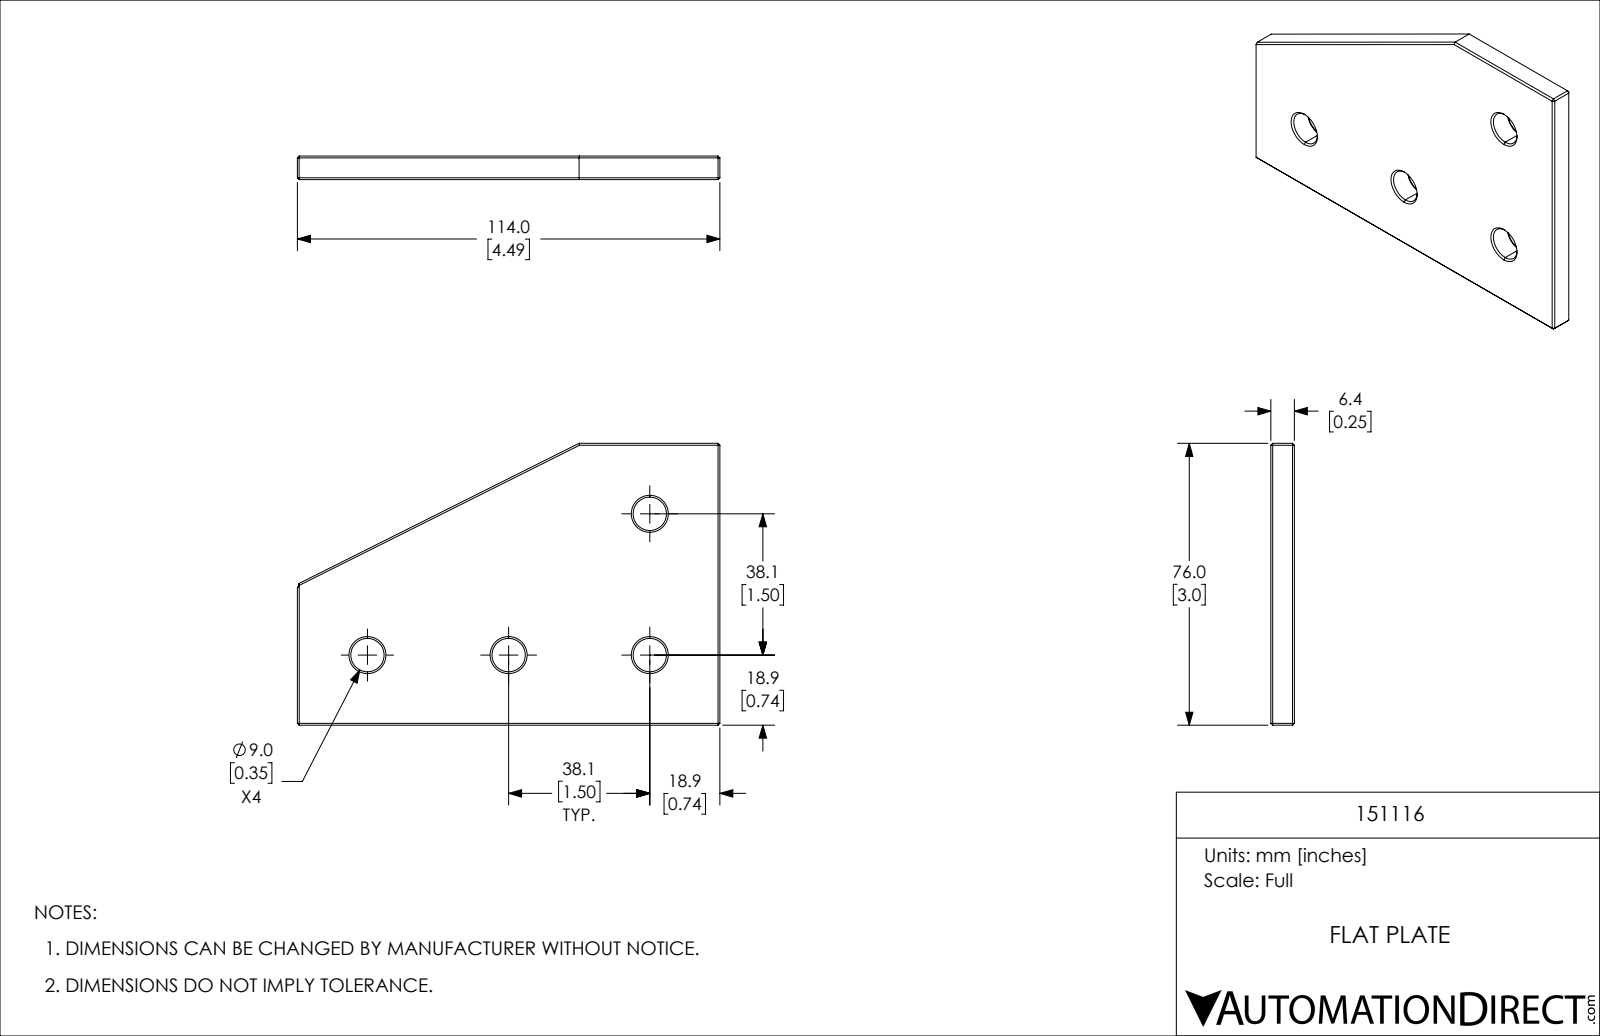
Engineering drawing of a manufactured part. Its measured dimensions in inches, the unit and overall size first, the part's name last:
Units: inches
Overall size (bounding box): 4.488 × 2.992 × 0.25
Round holes (diameter × count): ⌀0.354 ×4
Main face-to-face distances: 0.25, 2.992, 4.488, 2.265, 3.322, 5.261, 4.415, 4.415
Hole centre spacings: 1.5, 2.121, 3, 3.354
Volume: 2.692 in³ · Surface area: 25.73 in²
Bodies: 1 solid, 53 faces (29 planar, 8 cylindrical, 16 other)
Part name (STEP PRODUCT): 151116
STEP written by: SolidWorks 2021 (CONFIG_CONTROL_DESIGN)
